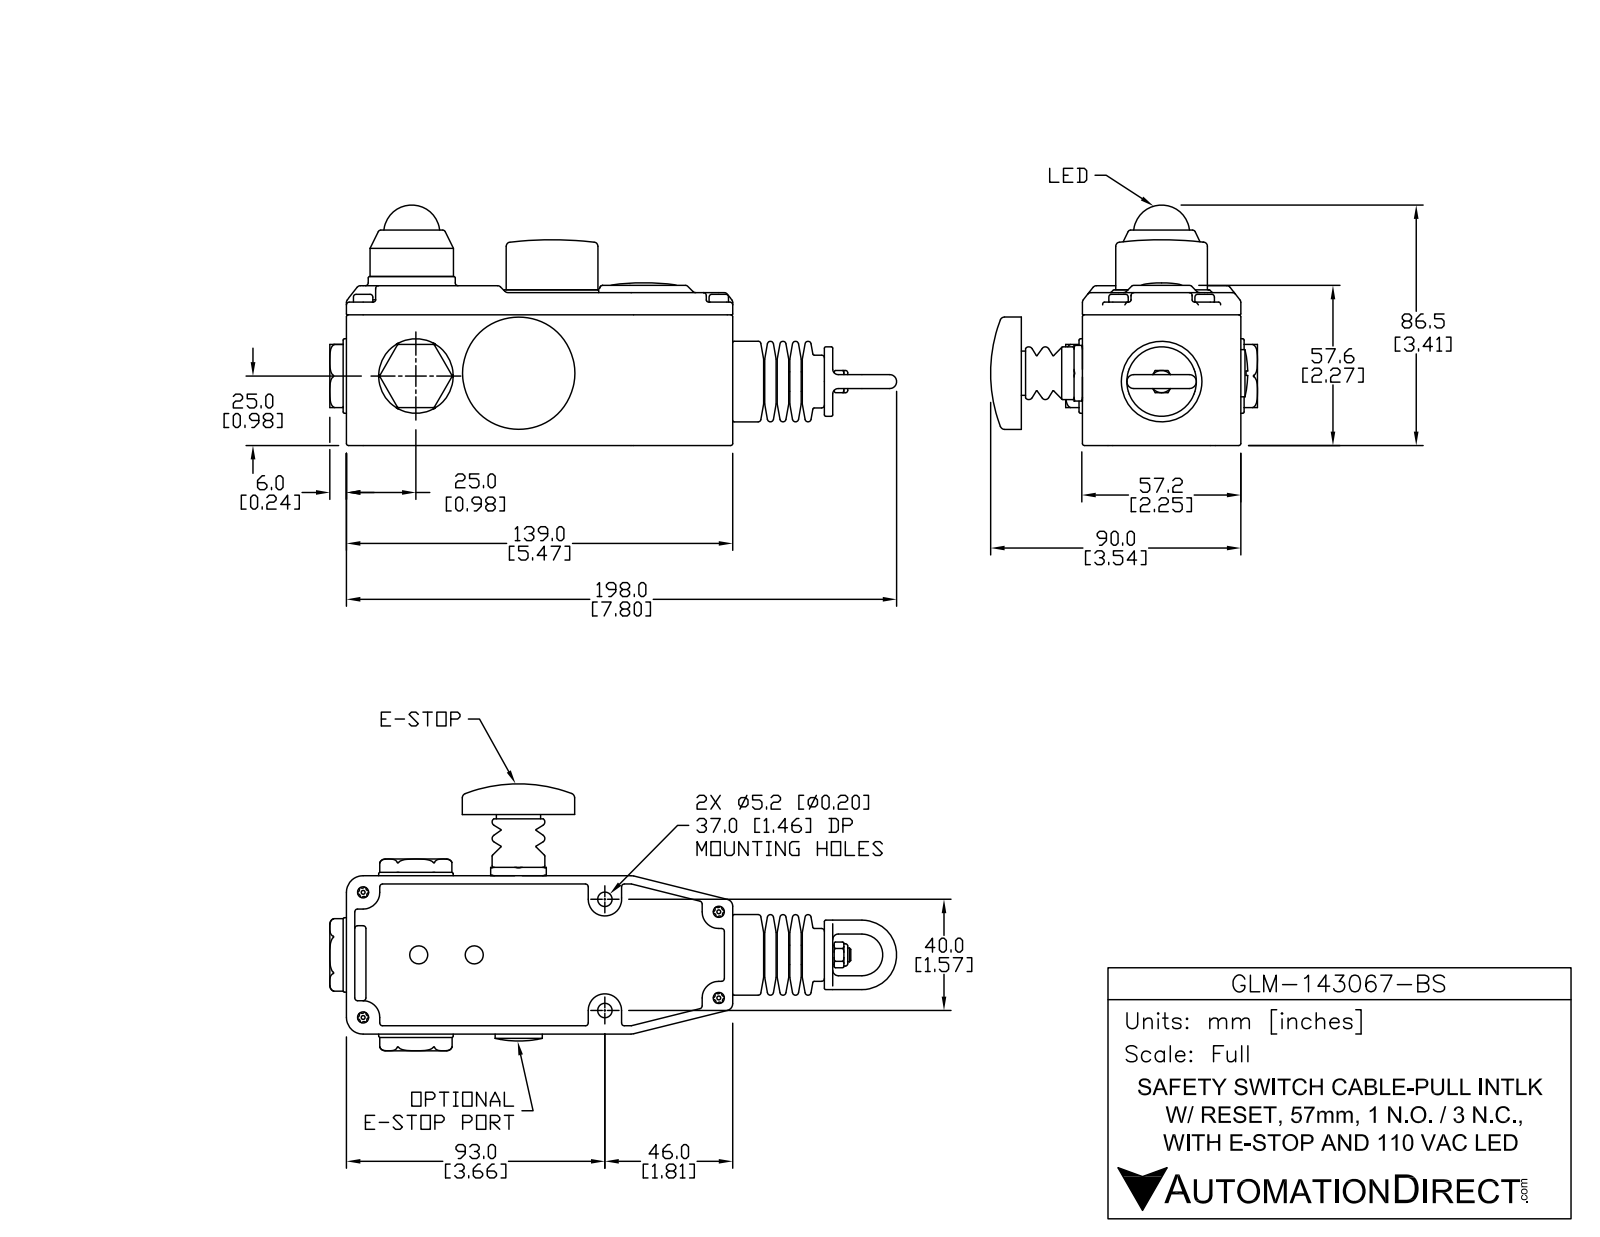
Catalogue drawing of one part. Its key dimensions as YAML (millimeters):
part_name: "GLM-143067-BS"
step_written_by: "SolidWorks 2013 (AUTOMOTIVE_DESIGN)"
units: millimeters
bodies: {solids: 1, faces: 442, planar: 132, cylindrical: 150, other: 160}
overall_size: [204, 96.5, 83.91]
volume: 486361
surface_area: 58860
round_holes:
  - {diameter: 4, count: 4}
  - {diameter: 5.2, count: 2}
  - {diameter: 21, count: 1}
  - {diameter: 34, count: 1}
round_bosses_or_shafts:
  - {diameter: 7, count: 5}
  - {diameter: 26.8, count: 2}
  - {diameter: 5, count: 2}
  - {diameter: 40, count: 1}
  - {diameter: 33, count: 1}
  - {diameter: 31.3, count: 1}
  - {diameter: 30, count: 1}
  - {diameter: 29, count: 1}
partial_cylinders:
  - {radius: 0.16, count: 31}
  - {radius: 0.5, count: 31}
  - {radius: 1, count: 4}
  - {radius: 5.2, count: 4}
  - {radius: 7, count: 2}
  - {radius: 13, count: 2}
face_to_face_distances: [57.2, 54.68, 57.18, 2.5, 57.5, 55, 0.32, 139, 6.3, 63.5]
hole_center_spacings: [28.53, 28.66, 31, 40, 41.24, 41.25, 45, 54.21]
